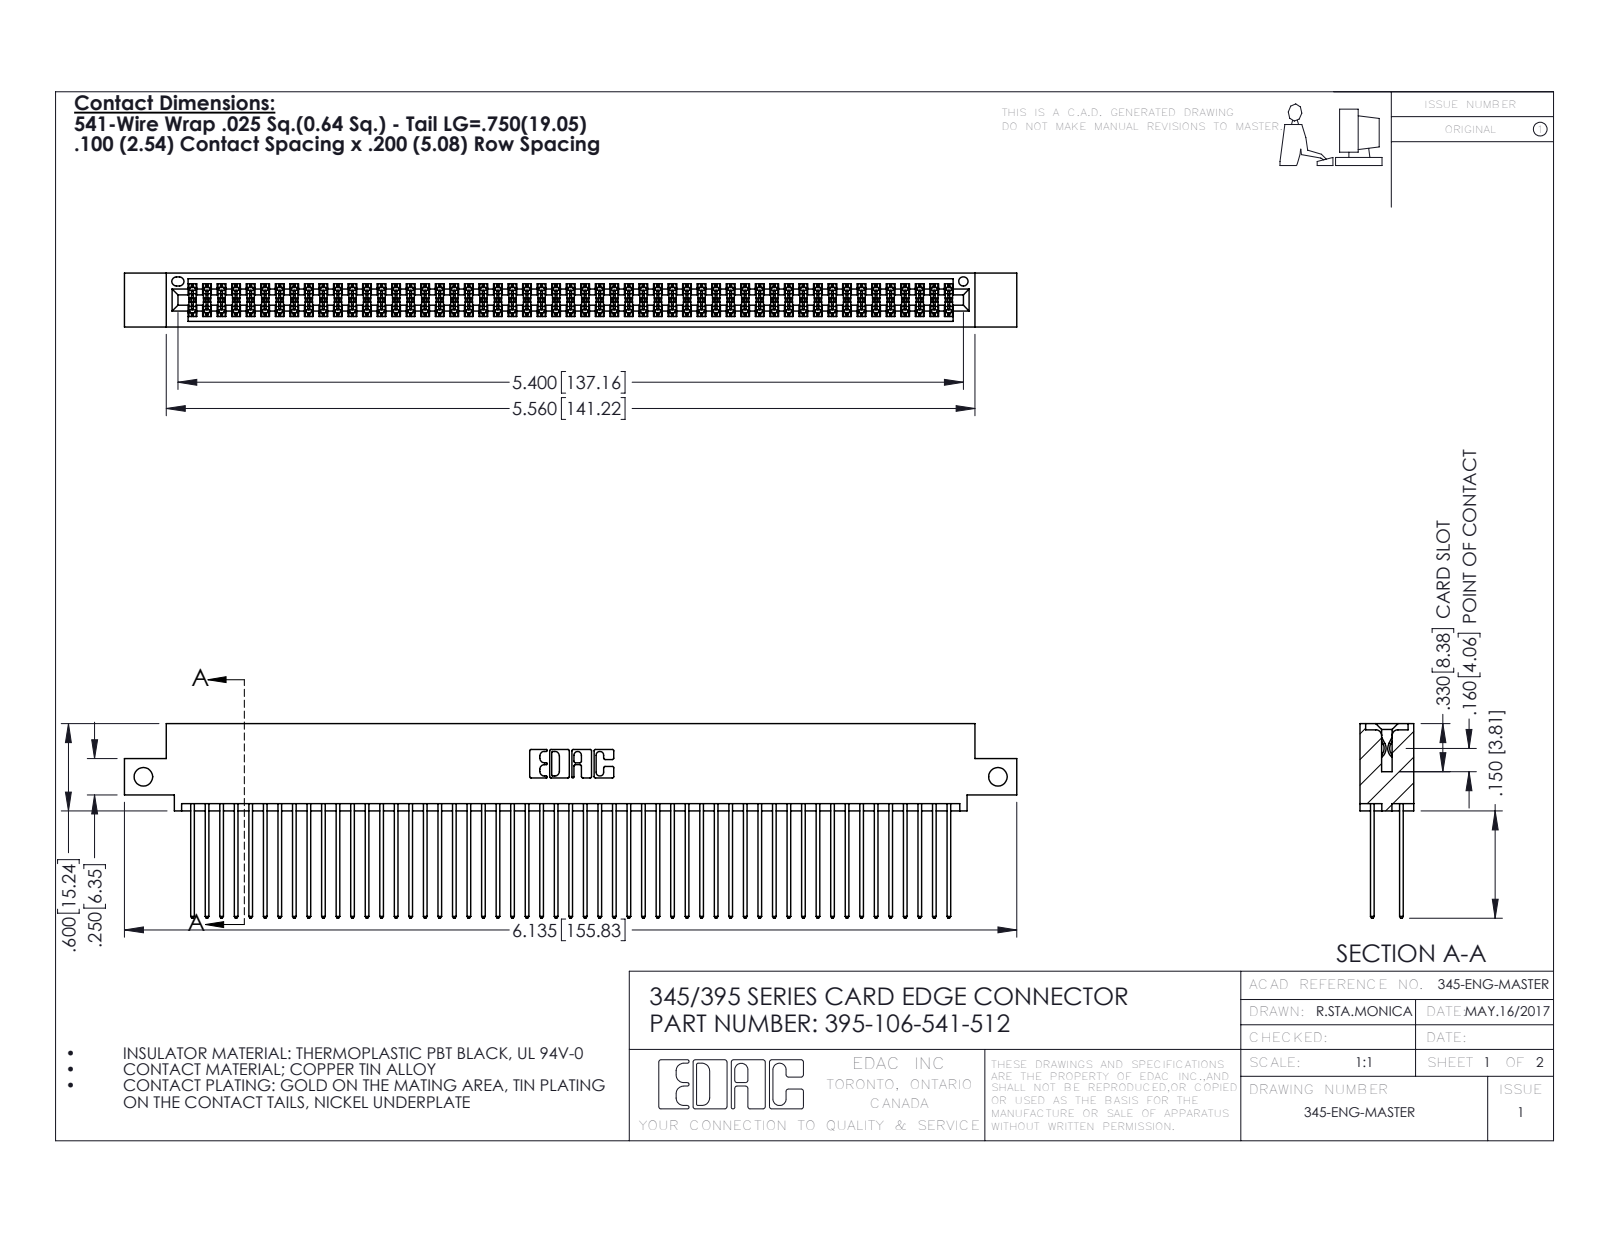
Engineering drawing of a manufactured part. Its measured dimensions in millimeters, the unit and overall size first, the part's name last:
Units: millimetres
Overall size (bounding box): 155.8 × 34 × 9.4
Round holes (diameter × count): ⌀3.3 ×2, ⌀1.6 ×1
Partial cylindrical surfaces — rounded edges, fillets, slot ends (radius × count): R0.2 ×159, R0.3 ×106, R0.3 ×22, R0.2 ×6, R0.8 ×6, R0.7 ×3, R0.4 ×2, R0.5 ×2
Main face-to-face distances: 7.6, 1.8, 5.1, 2.5, 6.9, 0.6, 5.7, 9.4, 4.4, 3.8
Hole centre spacings: 149.2
Volume: 15 700 mm³ · Surface area: 26 220 mm²
Bodies: 107 solids, 5430 faces (3582 planar, 1848 cylindrical, 0 other)
Part name (STEP PRODUCT): 345 Part_0.110 Offset - Side Mount; 345-292-001_345-293-141; 395-106-541-512
STEP written by: SolidWorks 2016 (CONFIG_CONTROL_DESIGN)
